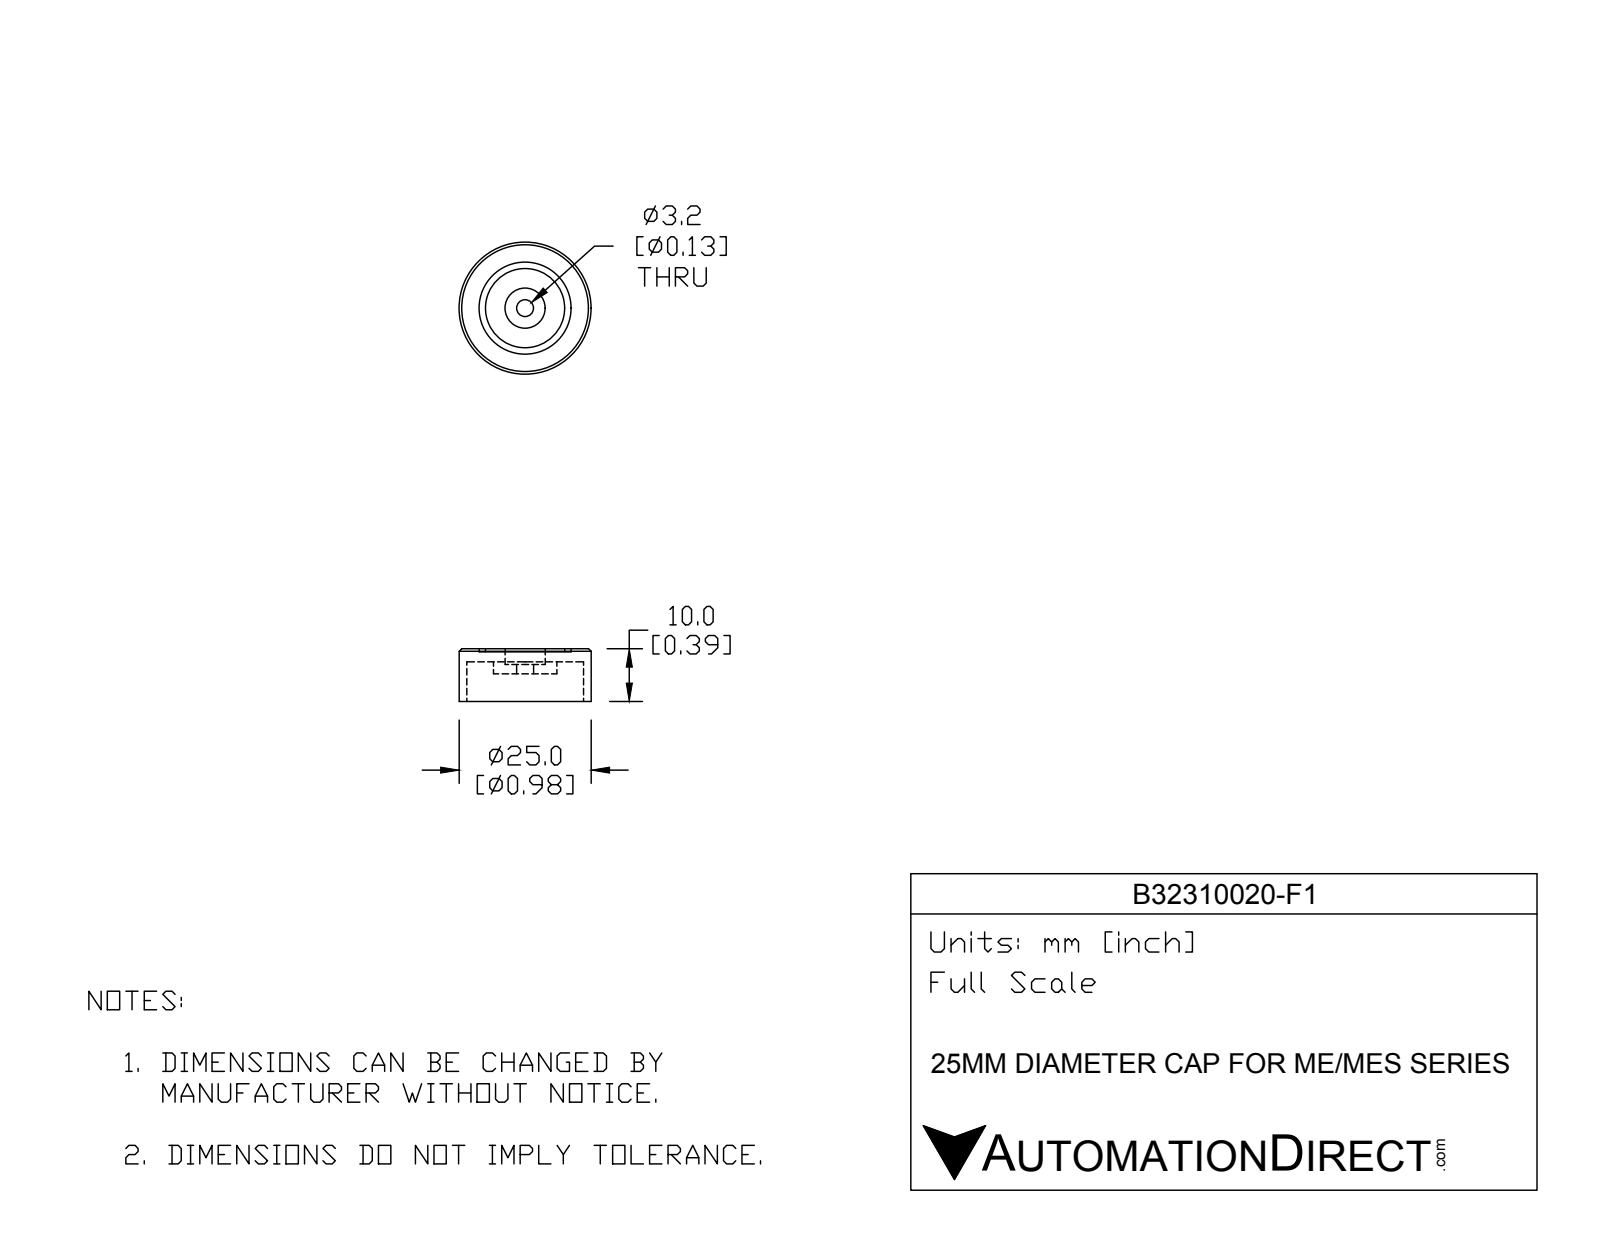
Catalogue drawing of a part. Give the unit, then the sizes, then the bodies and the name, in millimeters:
Units: millimetres
Overall size (bounding box): 25 × 25 × 10
Round holes (diameter × count): ⌀3.2 ×1, ⌀7.6 ×1, ⌀17.4 ×1, ⌀22.1 ×1
Round bosses / shafts (diameter × count): ⌀25 ×1, ⌀15 ×1, ⌀12 ×1
Main face-to-face distances: 2.5, 7.5, 10, 5.25, 2.25, 4.75, 9.4, 4.15, 1.9, 0.6
Volume: 2 090 mm³ · Surface area: 2 484 mm²
Bodies: 1 solid, 23 faces (7 planar, 14 cylindrical, 2 other)
Part name (STEP PRODUCT): B32310020-F1
STEP written by: SolidWorks 2016 (AUTOMOTIVE_DESIGN)
